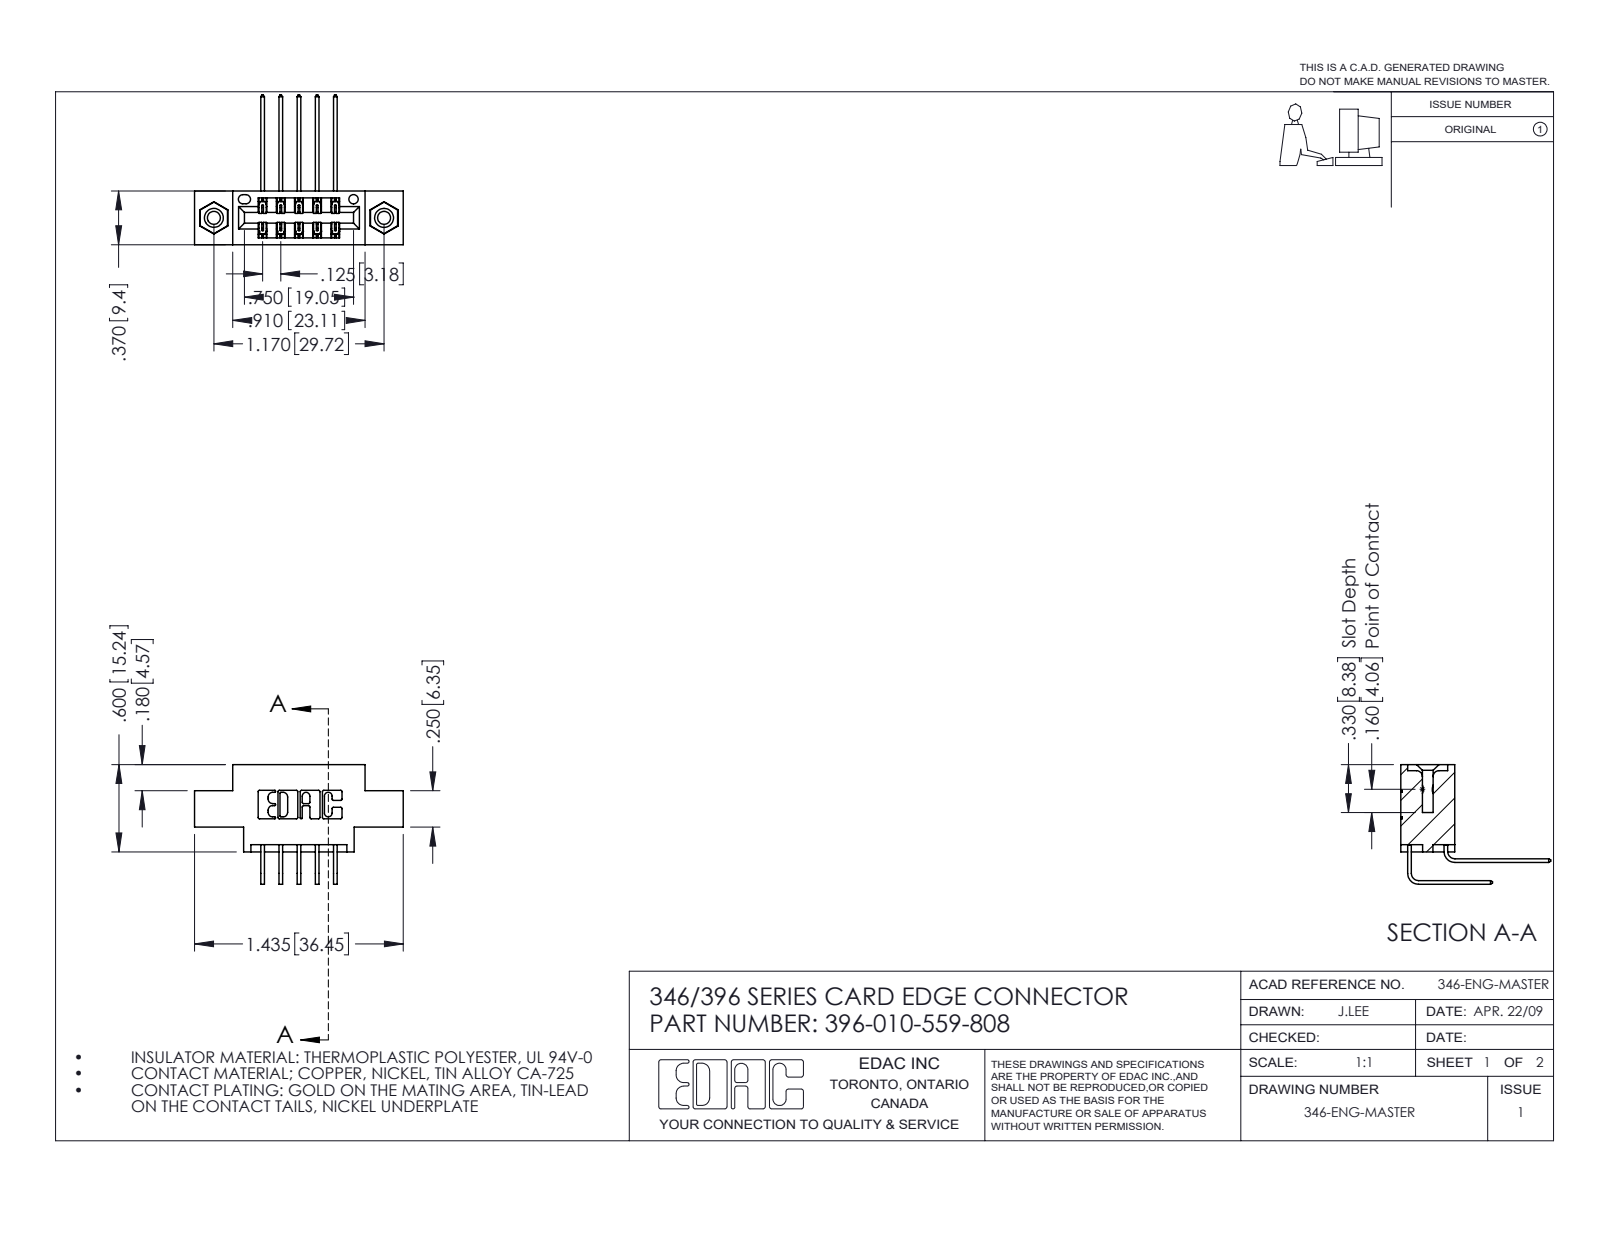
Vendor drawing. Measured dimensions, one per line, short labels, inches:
name: 345-292-001_558 559 Tail - 1; 346 Part_0.170 Offset - 0.156 Dia-TI; 345-250-001_345-250-003-102; 345-292-001_559 Tail - 2 (+1 more)
written by: SolidWorks 2016 (CONFIG_CONTROL_DESIGN)
unit: in
bodies: 13 solids, 726 faces (482 planar, 228 cylindrical, 16 other)
size: 1.435 × 1.03 × 0.823
volume: 0.193 in³; area: 6.577 in²
holes: 2× ⌀0.089, 2× ⌀0.125, 2× ⌀0.156, 1× ⌀0.064
bosses: 2× ⌀0.155
rounds: 22× R0.01, 15× R0.006, 6× R0.007, 6× R0.031, 3× R0.026, 2× R0.014, 2× R0.022, 2× R0.024
face distances: 0.25, 0.37, 0.048, 0.322, 0.025, 0.072, 0.125, 0.222, 0.148, 0.125
hole spacings: 0.246, 0.969, 1.17
